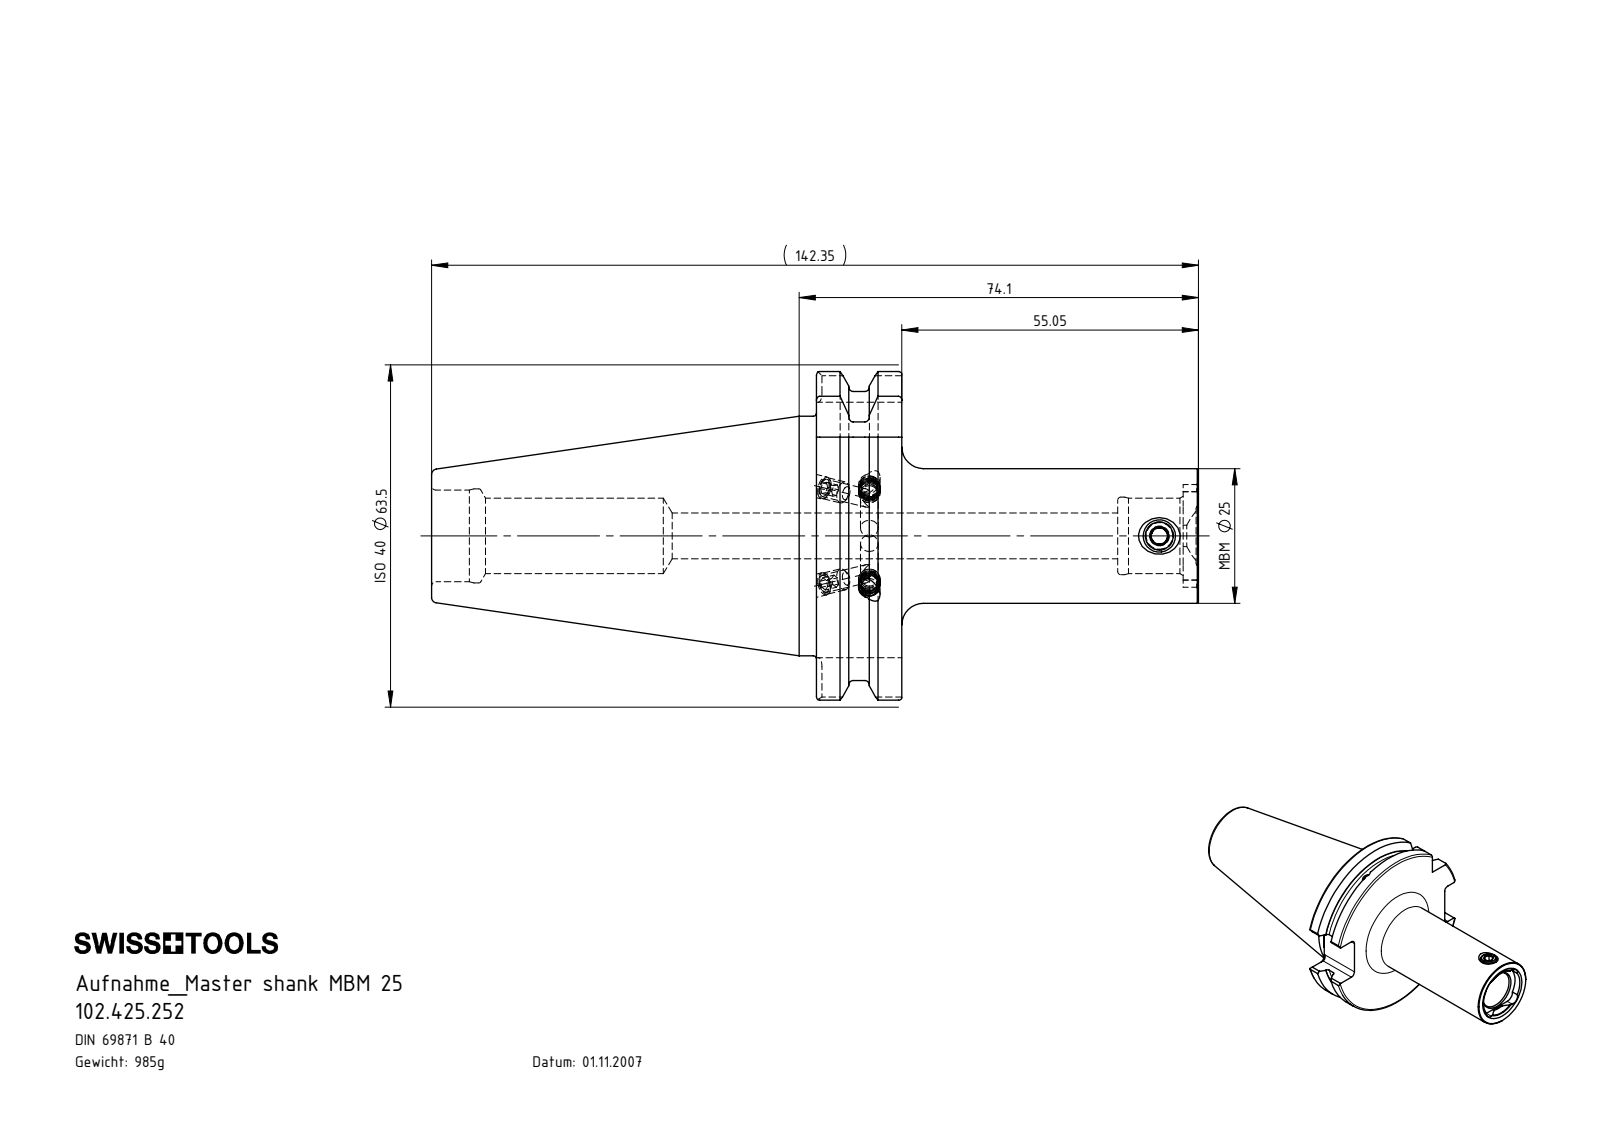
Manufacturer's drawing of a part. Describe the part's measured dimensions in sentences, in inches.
The part is named "102.425.252; KVT_MB_600_040; ISO 4026 - M4 x 5_PreviewCfg; MB2-ER1.001.008_A (+1 more)". Its 3-D file was written by "SolidWorks 2017 (CONFIG_CONTROL_DESIGN)". It is 8 solids with 299 faces: 77 planar, 88 cylindrical and 134 other. Overall it measures 5.604 by 2.5 by 2.399 inches. Its volume is 7.656 cubic inches and its surface area 41.56 square inches. Round holes: 3 of diameter 0.118, 3 of diameter 0.13, 2 of diameter 0.165, 1 of diameter 0.157, 1 of diameter 0.207, 1 of diameter 0.335, 1 of diameter 0.551, 1 of diameter 0.567, 1 of diameter 0.669, 1 of diameter 0.687. Round bosses or shafts: 4 of diameter 0.157, 1 of diameter 1.75, 1 of diameter 0.984, 1 of diameter 0.236. Partial cylindrical surfaces (rounded edges, fillets, slot ends): 8 of radius 0.063, 4 of radius 0.106, 1 of radius 0.315, 1 of radius 0.375, 1 of radius 1.102, 1 of radius 1.25. The main face-to-face distances are 0.624, 1.866, 2.791, 2.167, 2.813, 3.437, 5.604, 0.634, 5.492, 2.679.
